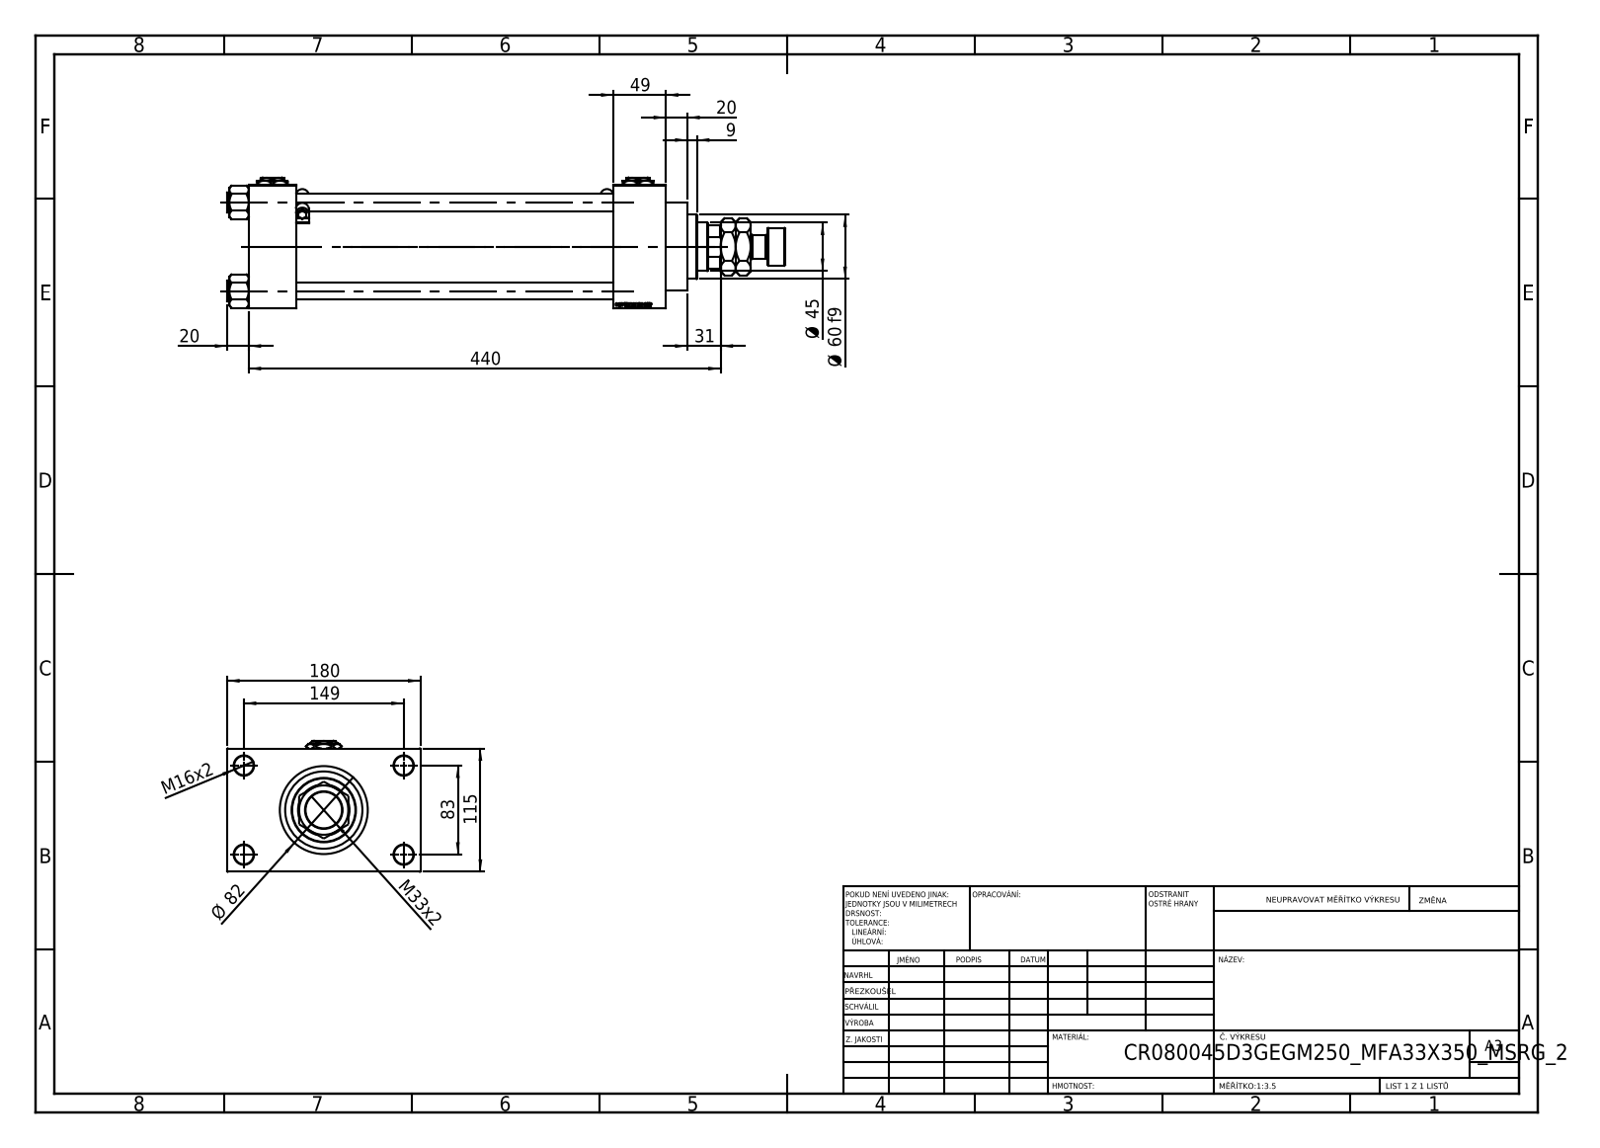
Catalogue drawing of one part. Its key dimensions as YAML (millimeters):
part_name: "V215CR_D_TYCINKA; V215_VC_A; MSRF_MSRG1; Zatka_pro_OIL_PORT (+4 more)"
step_written_by: "SolidWorks 2019 (CONFIG_CONTROL_DESIGN)"
units: millimeters
bodies: {solids: 16, faces: 1369, planar: 645, cylindrical: 132, other: 592}
overall_size: [520, 180, 122]
volume: 2819000
surface_area: 521705
round_holes:
  - {diameter: 16, count: 4}
  - {diameter: 18, count: 4}
  - {diameter: 7, count: 2}
  - {diameter: 26.44, count: 2}
  - {diameter: 35, count: 2}
  - {diameter: 31.5, count: 1}
  - {diameter: 45, count: 1}
  - {diameter: 48, count: 1}
  - {diameter: 61, count: 1}
  - {diameter: 72, count: 1}
  - {diameter: 80, count: 1}
round_bosses_or_shafts:
  - {diameter: 19, count: 4}
  - {diameter: 5, count: 2}
  - {diameter: 2.5, count: 2}
  - {diameter: 86, count: 1}
  - {diameter: 82, count: 1}
  - {diameter: 60, count: 1}
  - {diameter: 35, count: 1}
  - {diameter: 22, count: 1}
partial_cylinders:
  - {radius: 0.5, count: 12}
  - {radius: 6, count: 4}
  - {radius: 22, count: 1}
face_to_face_distances: [115, 296, 345, 49, 44, 340, 389, 32.5, 147.5, 180]
hole_center_spacings: [33.15, 58.48, 82.7, 85.28, 89.24, 115.85, 142.43, 83]
